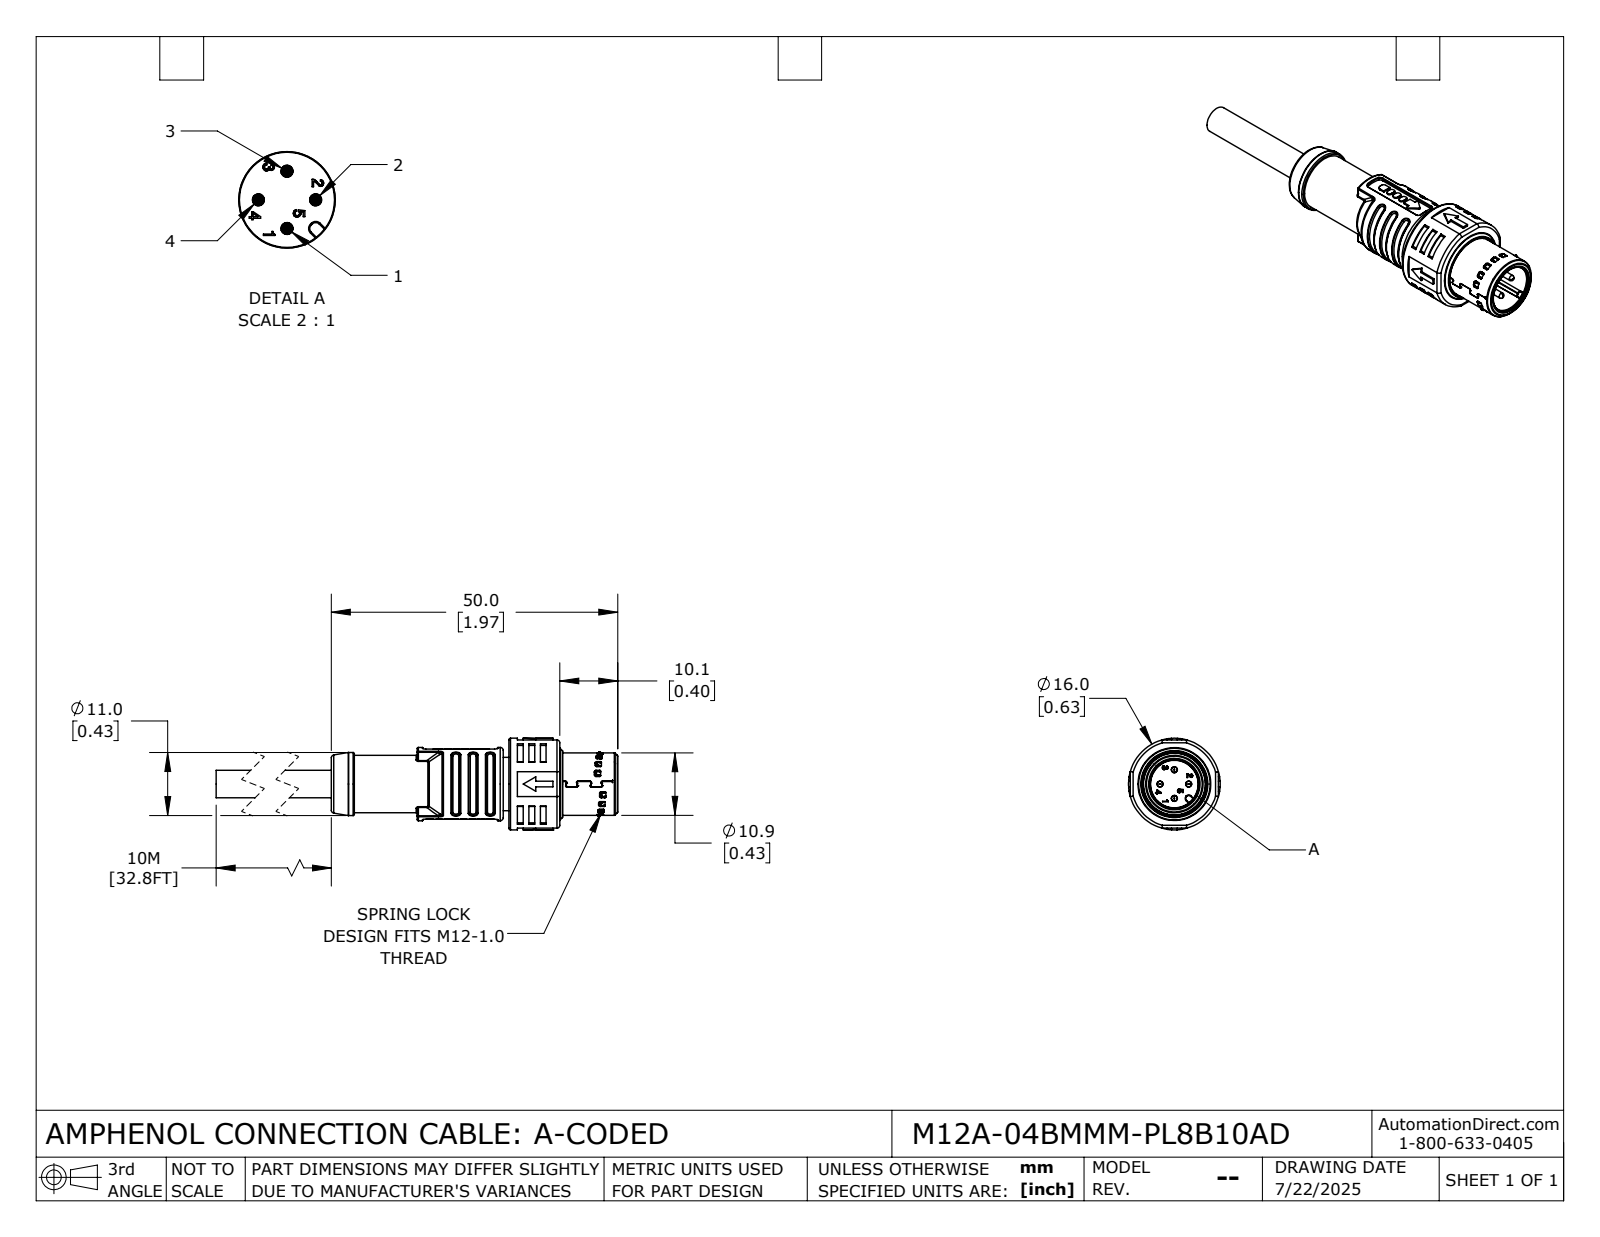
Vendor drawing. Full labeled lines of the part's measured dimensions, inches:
Part name (STEP PRODUCT): M12A-04BMMM-PL8B10AD
STEP written by: SolidWorks 2024 (CONFIG_CONTROL_DESIGN)
Units: inches
Bodies: 1 solid, 2276 faces (1081 planar, 672 cylindrical, 523 other)
Overall size (bounding box): 2.862 × 0.63 × 0.63
Volume: 0.316 in³ · Surface area: 9.253 in²
Round holes (diameter × count): ⌀0.041 ×4, ⌀0.057 ×4, ⌀0.327 ×1, ⌀0.354 ×1, ⌀0.4 ×1, ⌀0.413 ×1, ⌀0.453 ×1, ⌀0.465 ×1, ⌀0.559 ×1
Round bosses / shafts (diameter × count): ⌀0.055 ×4, ⌀0.039 ×4, ⌀0.63 ×1, ⌀0.555 ×1, ⌀0.504 ×1, ⌀0.488 ×1, ⌀0.433 ×1, ⌀0.429 ×1
Partial cylindrical surfaces — rounded edges, fillets, slot ends (radius × count): R0.008 ×114, R0.01 ×66, R0.012 ×64, R0.006 ×44, R0.02 ×38, R0.005 ×12, R0.028 ×11, R0.004 ×10
Main face-to-face distances: 0.039, 0.398, 0.35, 0.339, 0.098, 0.059, 0.047, 1.28, 0.606, 1.618
Hole centre spacings: 0.098, 0.139, 0.197
